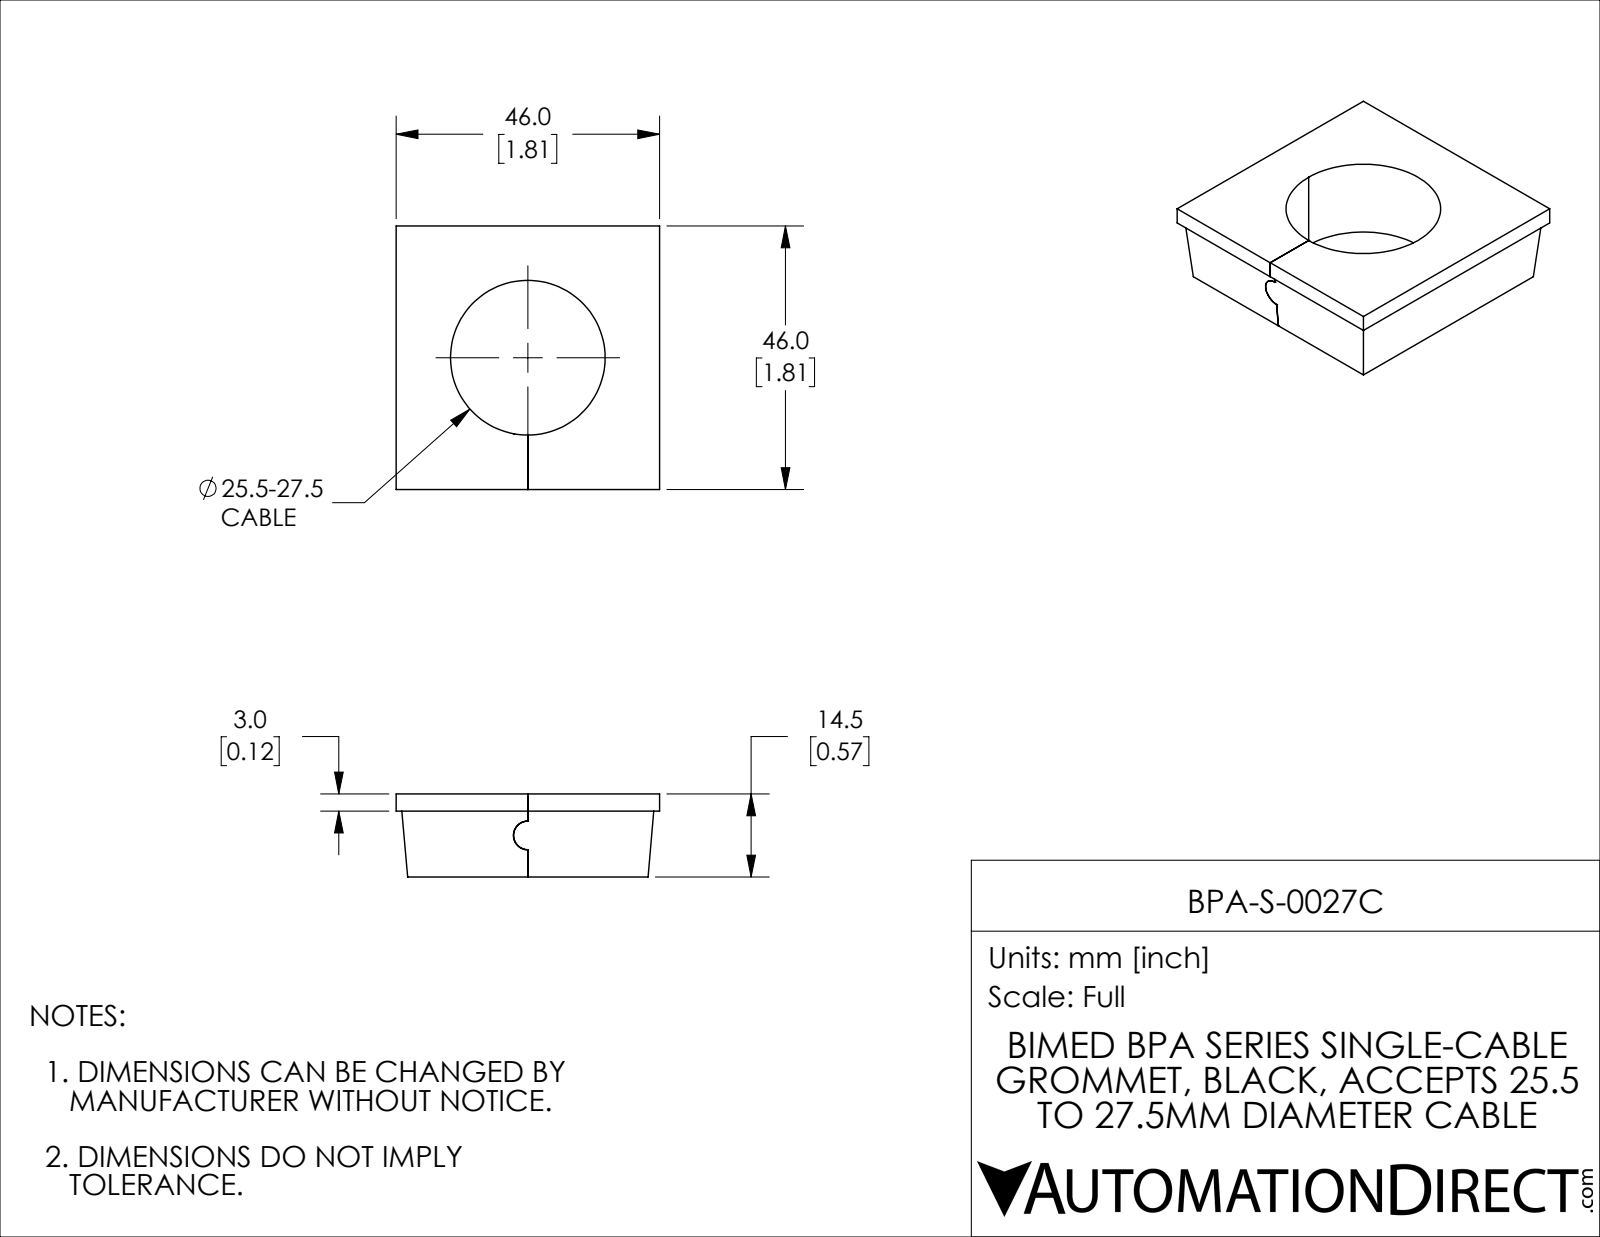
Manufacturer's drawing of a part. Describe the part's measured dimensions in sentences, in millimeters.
The part is named "BPA-S-0027C". Its 3-D file was written by "SolidWorks 2021 (CONFIG_CONTROL_DESIGN)". It is 1 solid with 22 faces: 17 planar, 5 cylindrical and 0 other. Overall it measures 46 by 46 by 14.5 millimeters. Its volume is 19 306 cubic millimeters and its surface area 6 969 square millimeters. Round holes: 1 of diameter 27. Partial cylindrical surfaces (rounded edges, fillets, slot ends): 1 of radius 2.5, 1 of radius 2.51. The main face-to-face distances are 14.5, 46, 11.5, 3, 22.99, 23.01.
